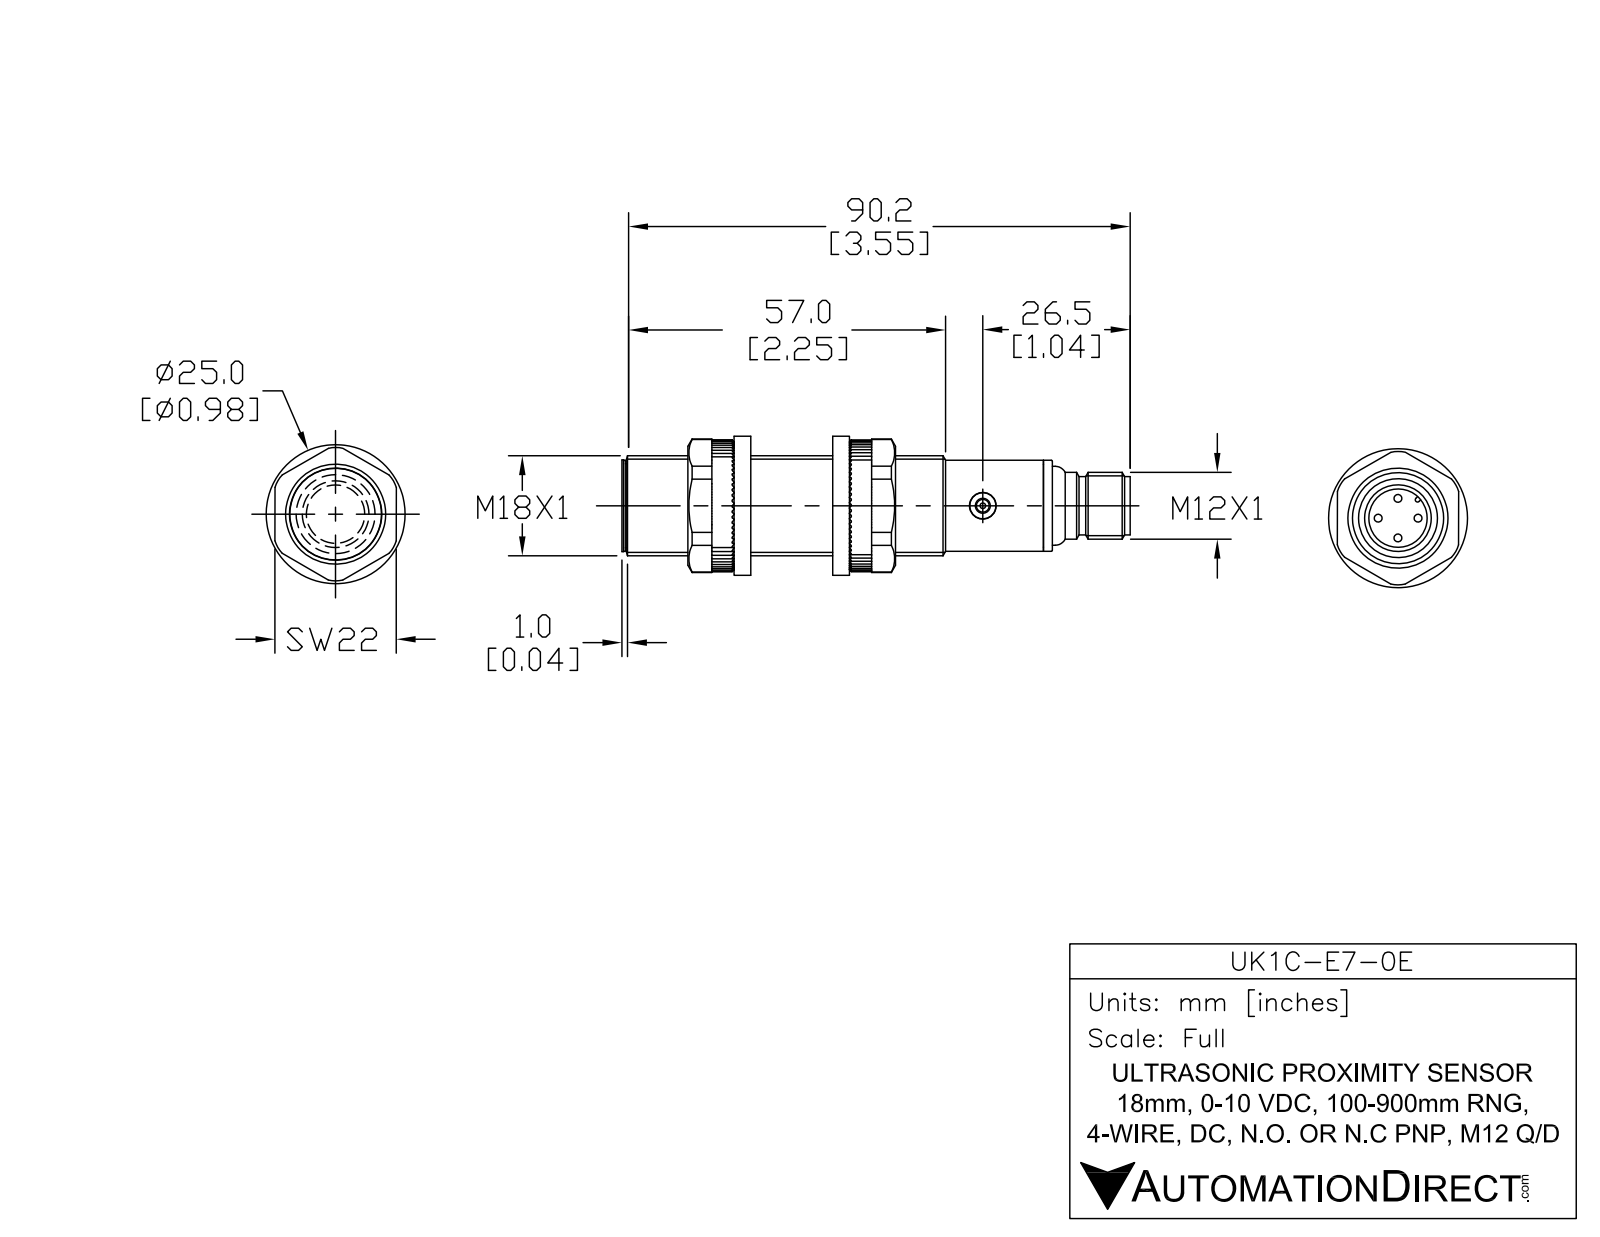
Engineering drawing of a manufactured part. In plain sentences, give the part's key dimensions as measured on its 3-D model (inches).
The part is named "UK1C-E7-0E". Its 3-D file was written by "SolidWorks 2017 (AUTOMOTIVE_DESIGN)". It is 6 solids with 106 faces: 21 planar, 48 cylindrical and 37 other. Overall it measures 3.606 by 0.709 by 0.709 inches. Its volume is 1.202 cubic inches and its surface area 10.68 square inches. Round holes: 1 of diameter 0.106, 1 of diameter 0.185, 1 of diameter 0.276, 1 of diameter 0.327, 1 of diameter 0.374. Round bosses or shafts: 4 of diameter 0.039, 1 of diameter 0.709, 1 of diameter 0.654, 1 of diameter 0.646, 1 of diameter 0.622, 1 of diameter 0.559, 1 of diameter 0.472, 1 of diameter 0.413. Partial cylindrical surfaces (rounded edges, fillets, slot ends): 1 of radius 0.024. The main face-to-face distances are 2.957, 0.039, 2.996, 0.037, 2.994, 0.043, 0.157, 3.055, 3.053, 3.016.
